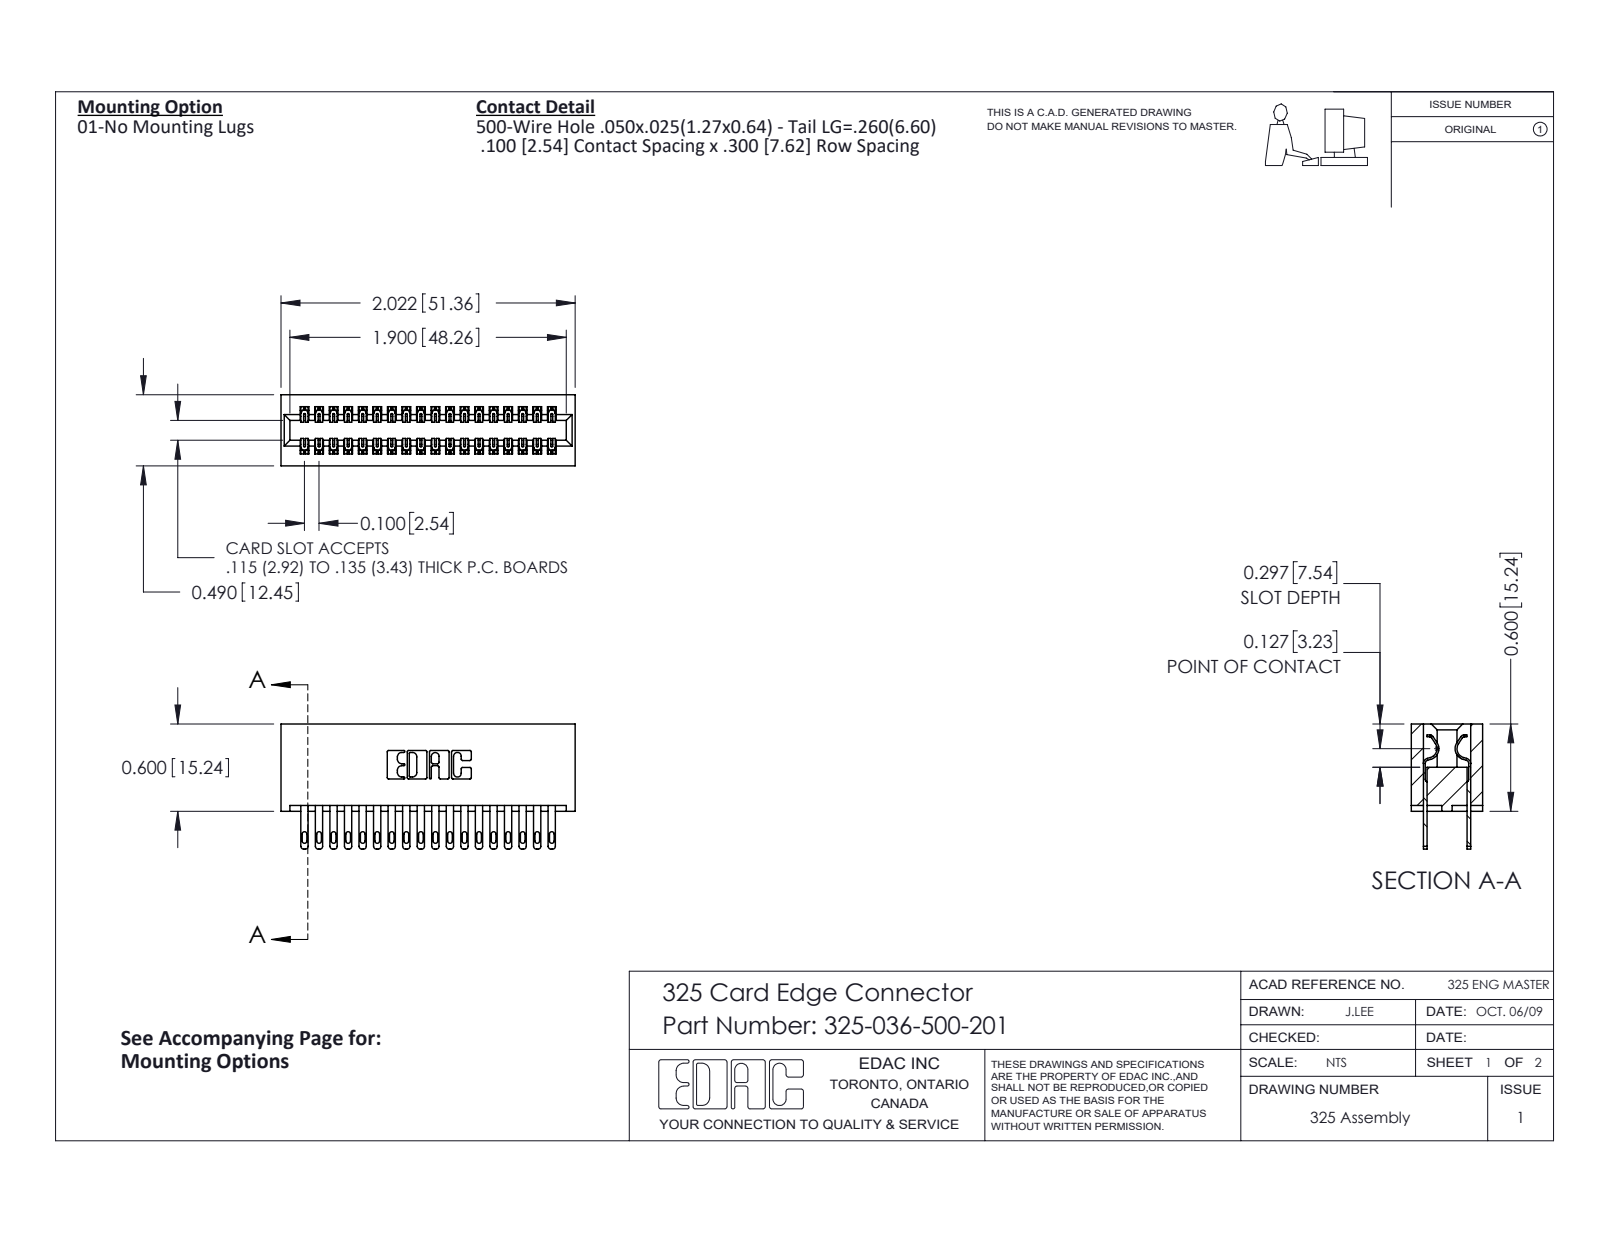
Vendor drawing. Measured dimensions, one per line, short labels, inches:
name: 325 Part_Lugless; 325-036-500-201; 325-292-001_325-293-100
written by: SolidWorks 2016 (CONFIG_CONTROL_DESIGN)
unit: in
bodies: 37 solids, 1834 faces (1146 planar, 688 cylindrical, 0 other)
size: 2.022 × 0.86 × 0.49
volume: 0.435 in³; area: 14.1 in²
rounds: 54× R0.006, 36× R0.016, 36× R0.02, 22× R0.01, 6× R0.007, 6× R0.031, 3× R0.026, 2× R0.014
face distances: 0.083, 0.407, 0.3, 0.107, 0.383, 0.025, 0.325, 0.49, 0.2, 0.1
